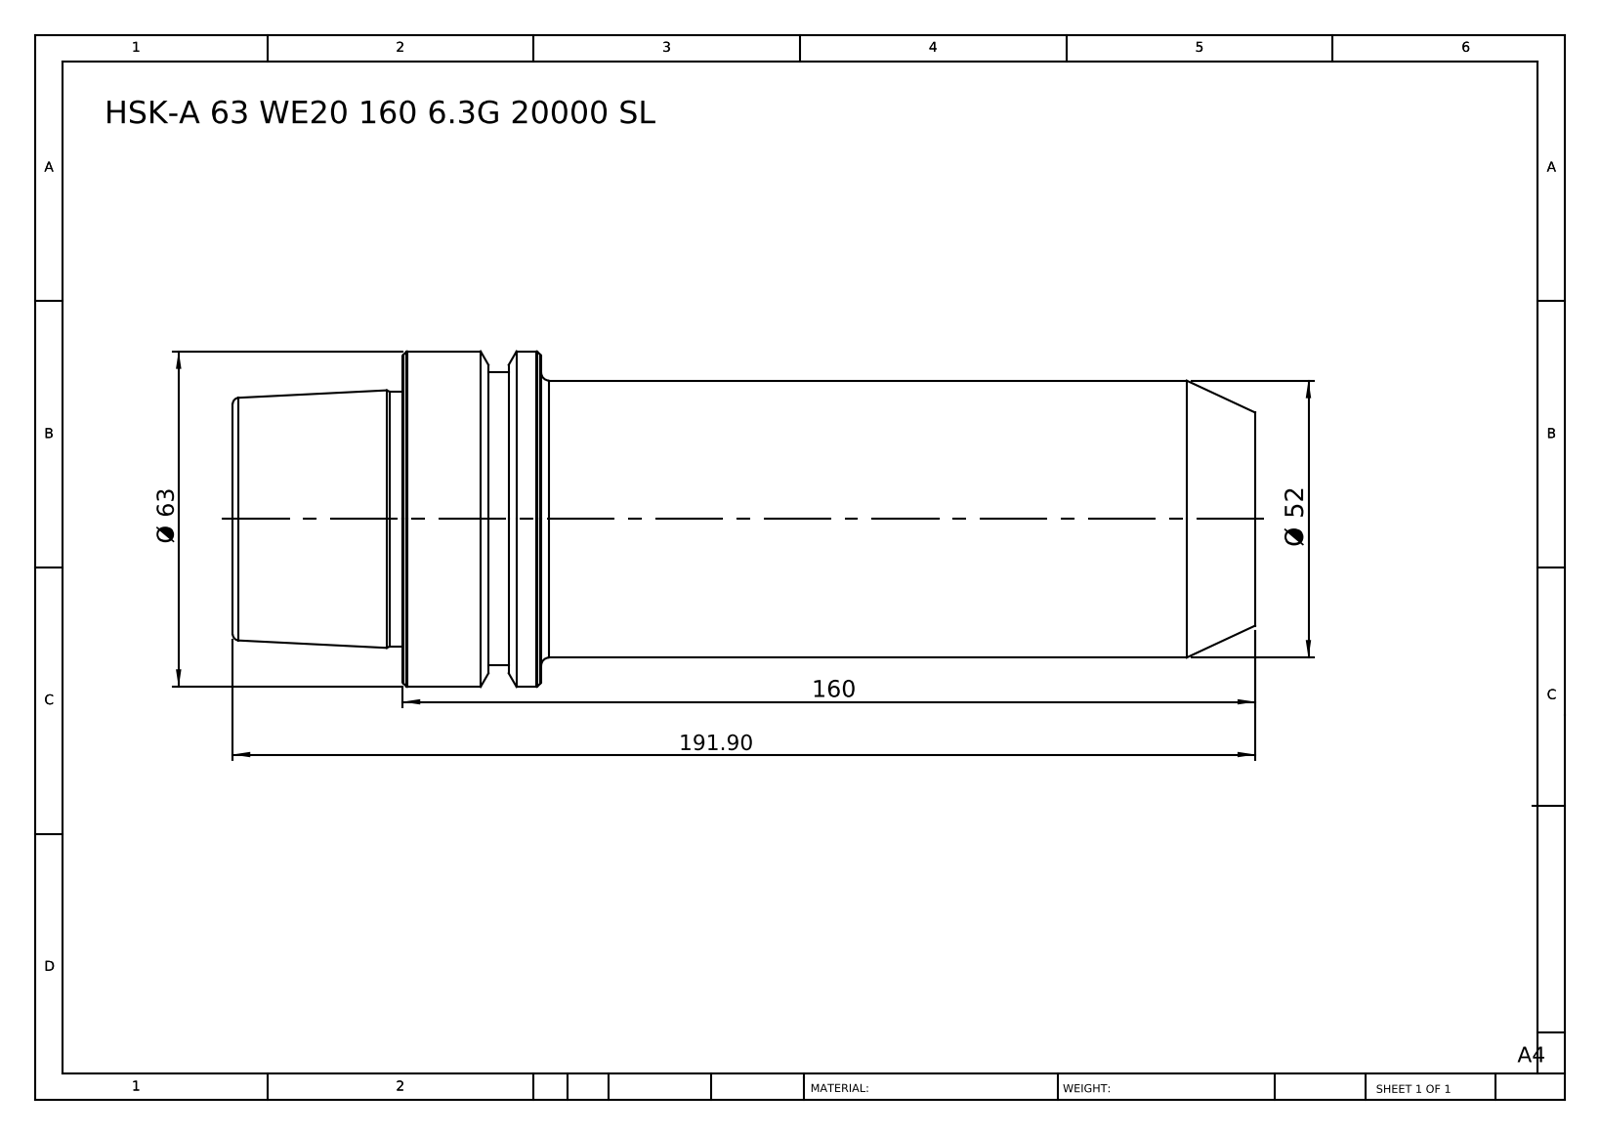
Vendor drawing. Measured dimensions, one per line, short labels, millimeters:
name: HSK-A 63 WE20 160 6.3G 20000 SL
written by: SolidWorks 2014 (CONFIG_CONTROL_DESIGN)
unit: mm
bodies: 1 solid, 46 faces (6 planar, 10 cylindrical, 30 other)
size: 191.9 × 63 × 63
volume: 411 409 mm³; area: 37 516 mm²
bosses: 1× ⌀63, 1× ⌀55, 1× ⌀52, 1× ⌀47.78
face distances: 191.9, 160, 31.9, 134, 26, 57.9, 140.1, 6.1, 19.9, 51.8
